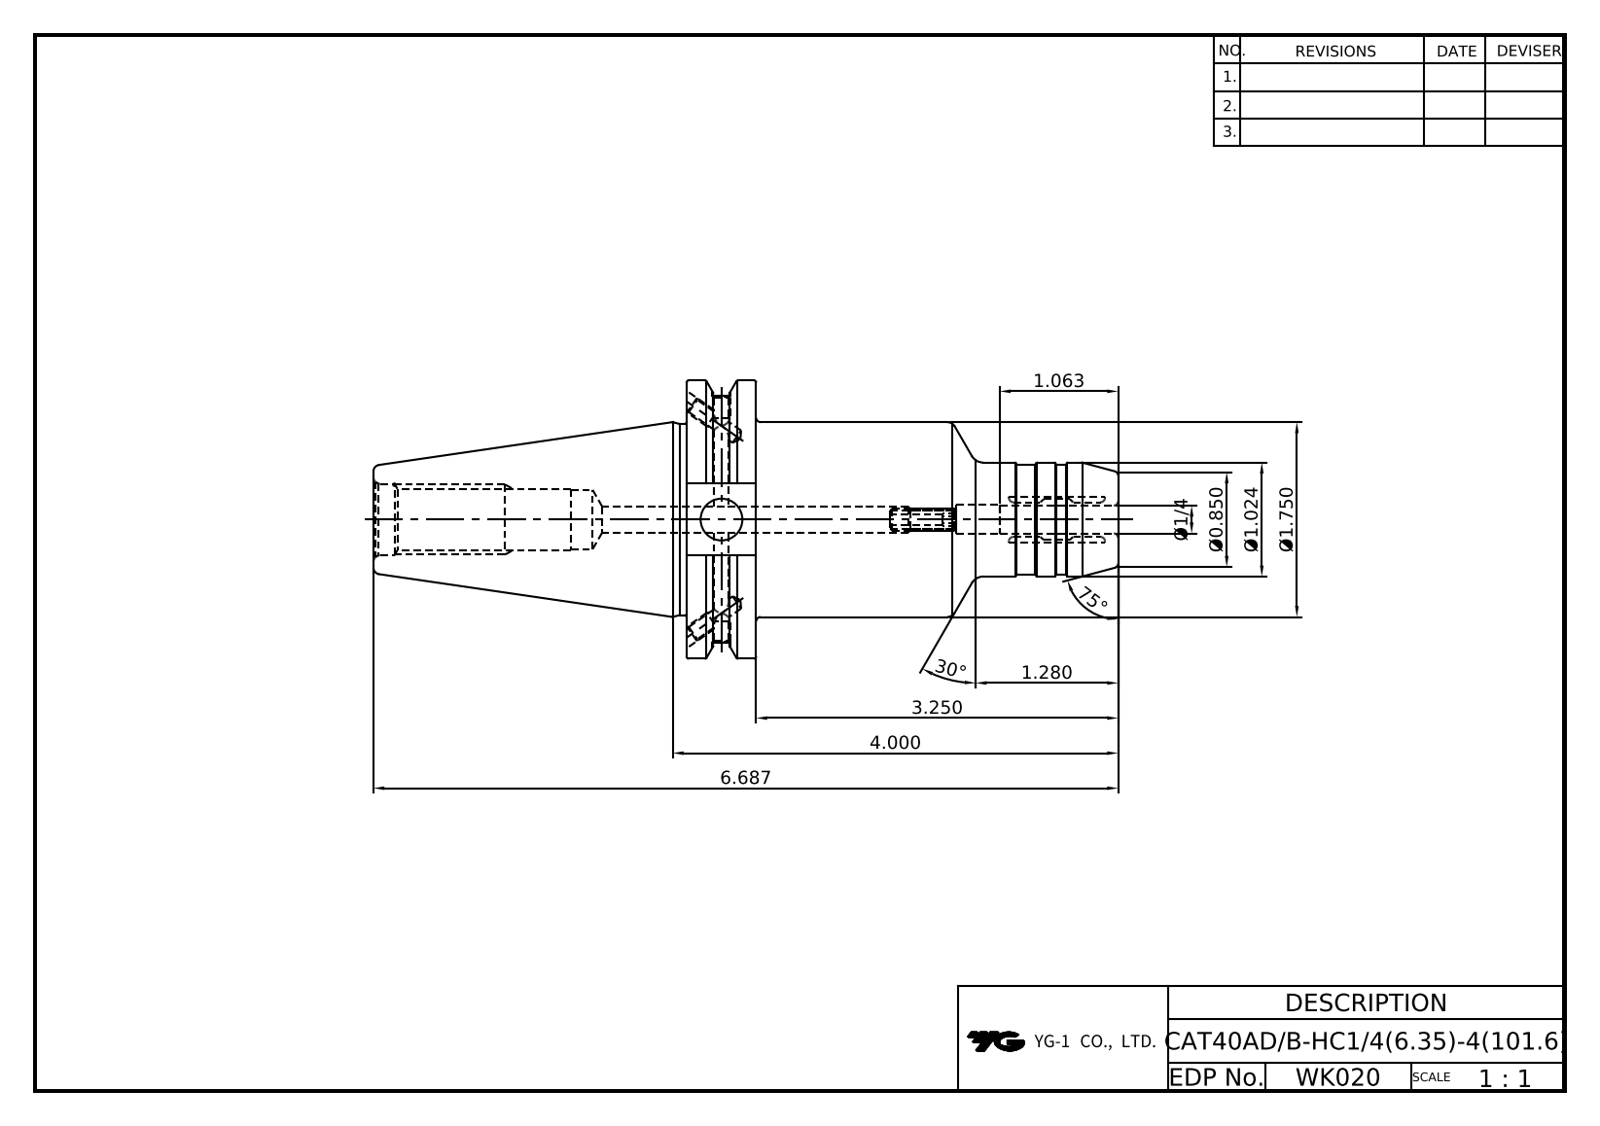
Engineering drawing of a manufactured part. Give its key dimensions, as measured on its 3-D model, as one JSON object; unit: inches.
{"part_name": "CAT40ADB-HMC12_7-5_9", "step_written_by": "CREO PARAMETRIC BY PTC INC, 2018500 (CONFIG_CONTROL_DESIGN)", "units": "inches", "bodies": {"solids": 1, "faces": 142, "planar": 36, "cylindrical": 38, "other": 68}, "overall_size": [6.688, 2.5, 2.395], "volume_in3": 11.82, "surface_area_in2": 49.31, "round_holes": [[0.165, 1], [0.197, 1], [0.236, 1], [0.25, 1], [0.268, 1], [0.375, 1], [0.531, 1], [0.625, 1], [0.642, 1]], "round_bosses_or_shafts": [[2.5, 1], [2.217, 1], [1.75, 1], [1.717, 1], [1.024, 1], [0.984, 1]], "face_to_face_distances": [0.626, 3.876, 3.25, 1.874, 2.812, 3.438, 6.688, 0.645, 3.05, 0.238]}
